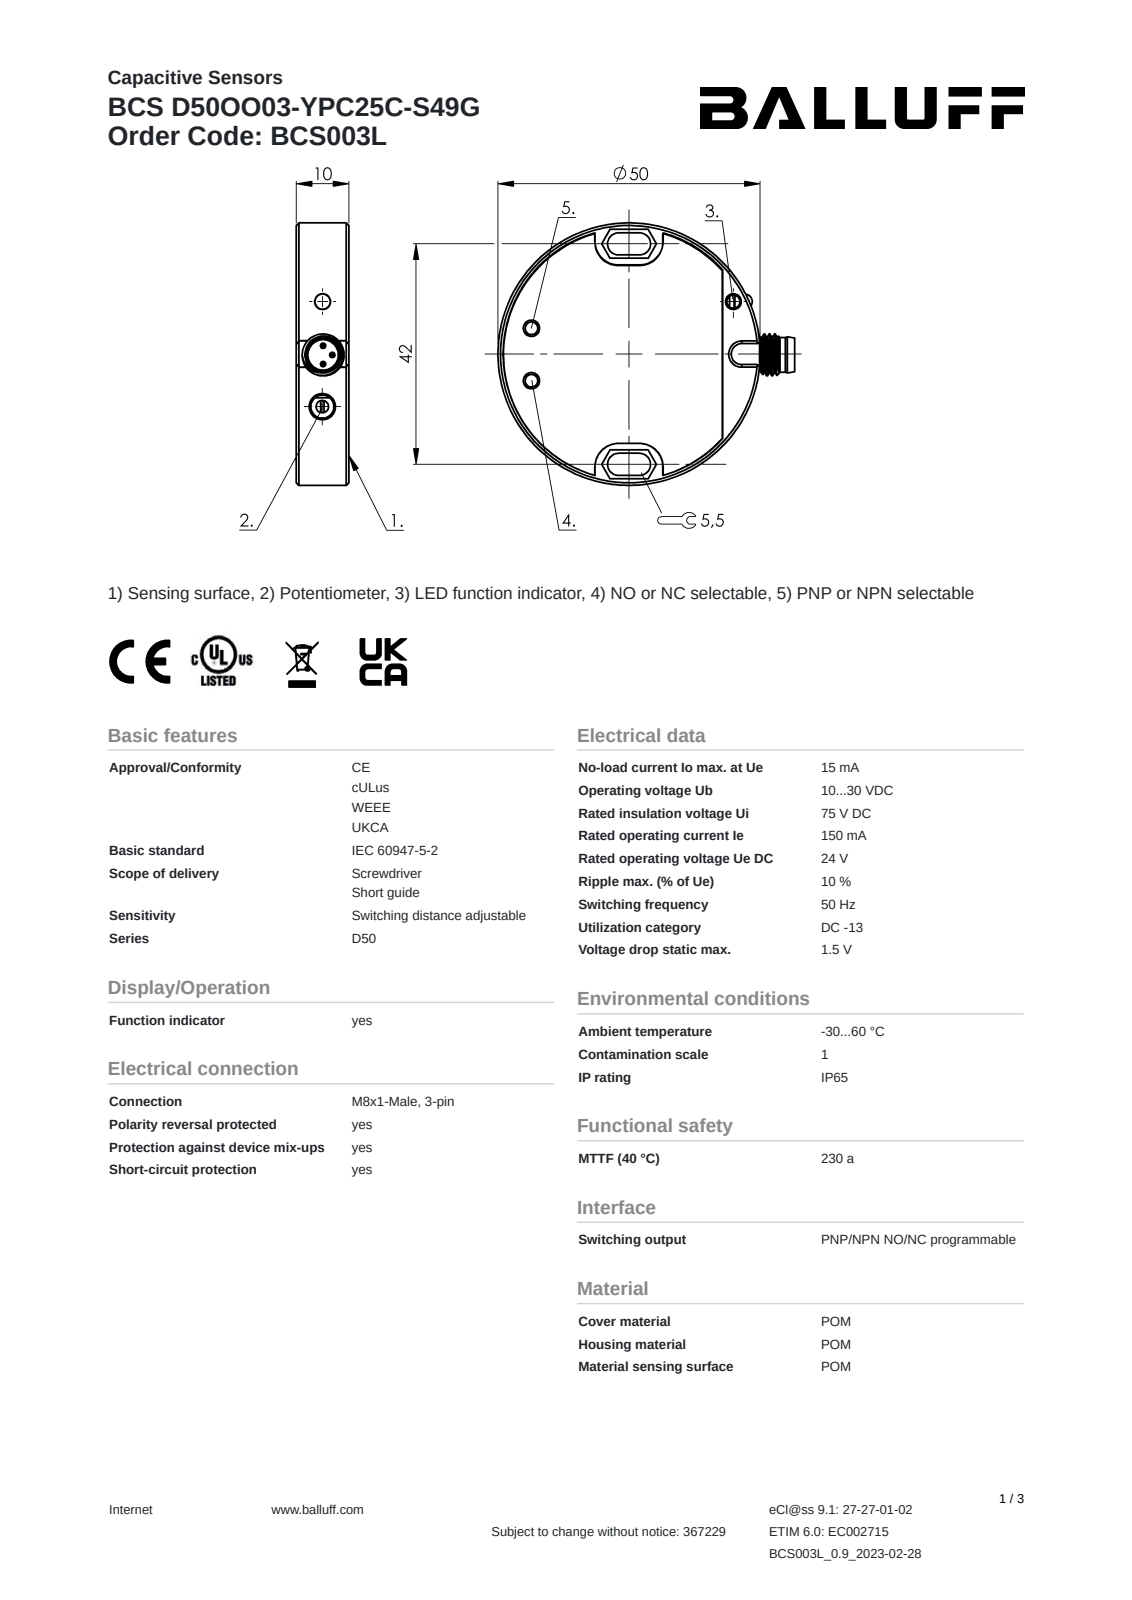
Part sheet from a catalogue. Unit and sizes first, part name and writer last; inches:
Units: inches
Overall size (bounding box): 2.23 × 1.969 × 0.394
Round holes (diameter × count): ⌀0.094 ×2, ⌀0.098 ×1, ⌀0.118 ×1, ⌀0.173 ×1, ⌀0.197 ×1, ⌀0.228 ×1, ⌀0.406 ×1, ⌀0.813 ×1, ⌀1.203 ×1
Round bosses / shafts (diameter × count): ⌀0.039 ×3, ⌀0.091 ×2, ⌀1.969 ×1, ⌀1.181 ×1, ⌀0.791 ×1, ⌀0.384 ×1, ⌀0.315 ×1, ⌀0.256 ×1
Partial cylindrical surfaces — rounded edges, fillets, slot ends (radius × count): R0.177 ×8, R0.02 ×4, R0.083 ×4, R0.079 ×1, R0.943 ×1, R0.945 ×1
Main face-to-face distances: 0.394, 1.654, 0.217, 0.355, 0.827, 0.144, 0.25, 0.392, 1.87, 1.437
Hole centre spacings: 0.394, 0.757, 0.787, 0.877, 1.528, 1.626
Volume: 1.138 in³ · Surface area: 10.26 in²
Bodies: 1 solid, 196 faces (120 planar, 64 cylindrical, 12 other)
Part name (STEP PRODUCT): BCS003L
STEP written by: SolidWorks 2021 (AUTOMOTIVE_DESIGN)
